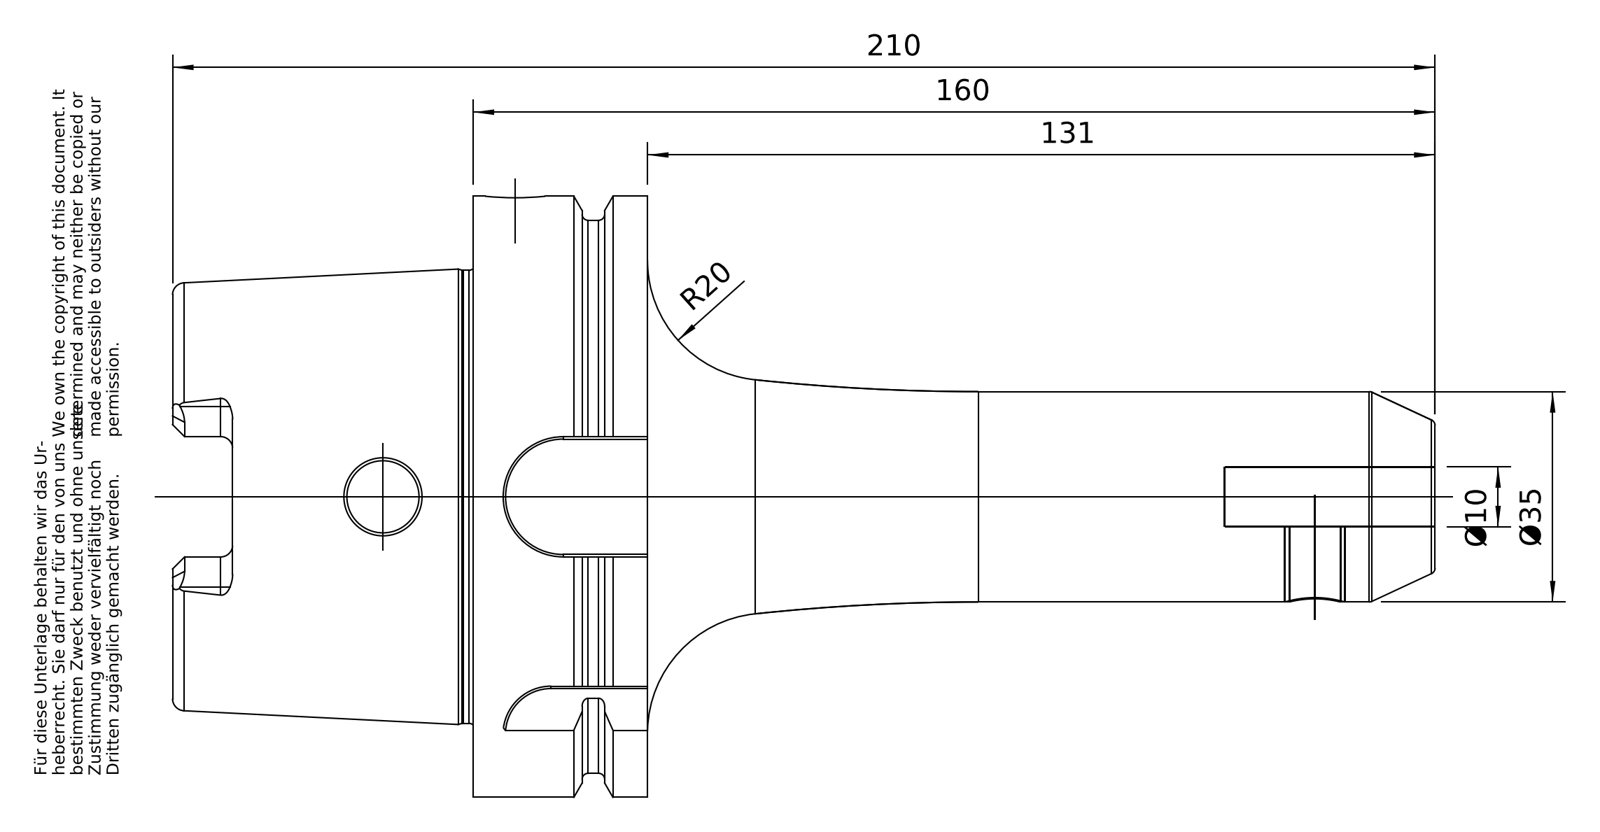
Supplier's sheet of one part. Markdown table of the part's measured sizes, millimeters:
| quantity | value |
| --- | --- |
| part name | A100-002-10 |
| STEP written by | PRO/ENGINEER BY PARAMETRIC TECHNOLOGY CORPORATION, 2010430 (CONFIG_CONTROL_DESIGN) |
| units | millimeters |
| bodies | 1 solid, 182 faces (50 planar, 55 cylindrical, 77 other) |
| overall size | 210 × 100 × 100 |
| volume | 393 564 mm³ |
| surface area | 65 154 mm² |
| round holes (diameter × count) | 10 × 3, 8.5 × 1, 12 × 1, 22.5 × 1, 24 × 1, 24.32 × 1, 24.5 × 1, 53 × 1, 63 × 1 |
| round bosses / shafts (diameter × count) | 100 × 1, 92 × 1, 75.36 × 1, 35 × 1 |
| partial cylindrical surfaces (radius × count) | 2 × 6, 5 × 4, 8 × 1, 10 × 1, 11 × 1 |
| main face-to-face distances | 29, 12.5, 16.5, 50, 62.5, 79, 160, 88, 78.5, 28.5 |
| hole center spacings | 133 |
